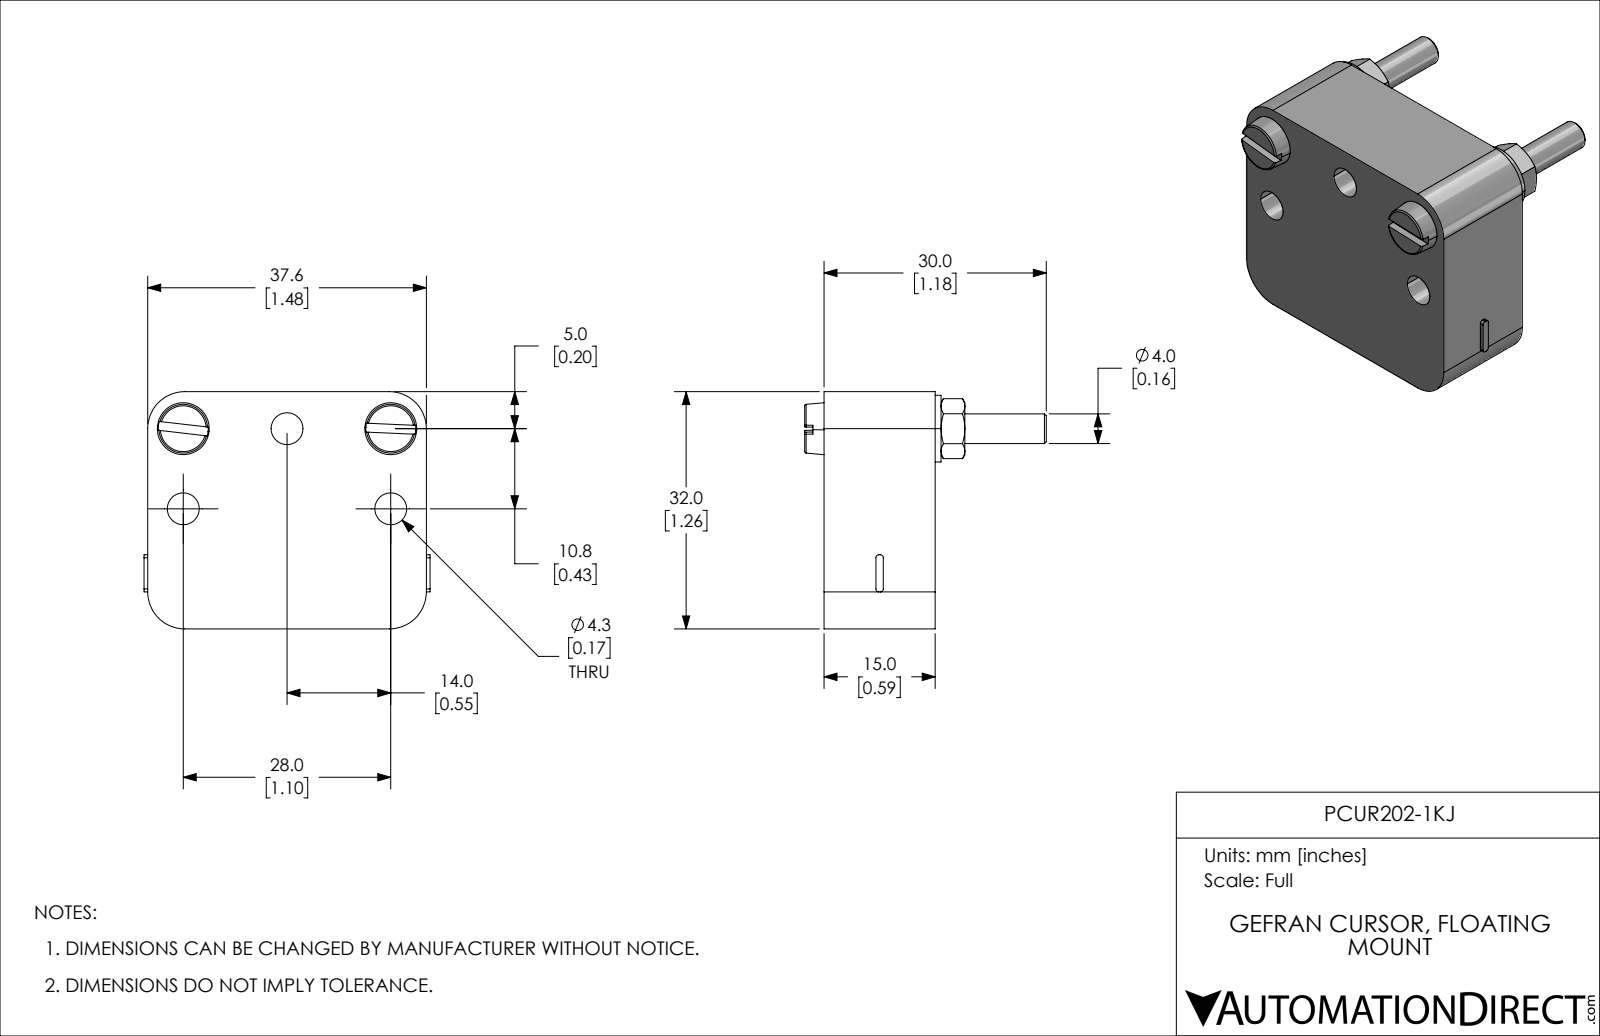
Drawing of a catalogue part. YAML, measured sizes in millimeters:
part_name: "PCUR202-1KJ"
step_written_by: "SolidWorks 2021 (CONFIG_CONTROL_DESIGN)"
units: millimeters
bodies: {solids: 7, faces: 124, planar: 50, cylindrical: 38, other: 36}
overall_size: [38.6, 32.6, 32]
volume: 17833
surface_area: 6839
round_holes:
  - {diameter: 4.3, count: 5}
  - {diameter: 4, count: 2}
round_bosses_or_shafts:
  - {diameter: 9, count: 2}
partial_cylinders:
  - {radius: 0.4, count: 4}
  - {radius: 5, count: 4}
face_to_face_distances: [15, 32, 37.6, 0.8, 15.8, 7, 3.2, 4, 19, 14]
hole_center_spacings: [10.8, 14, 17.68, 28, 30.01]
